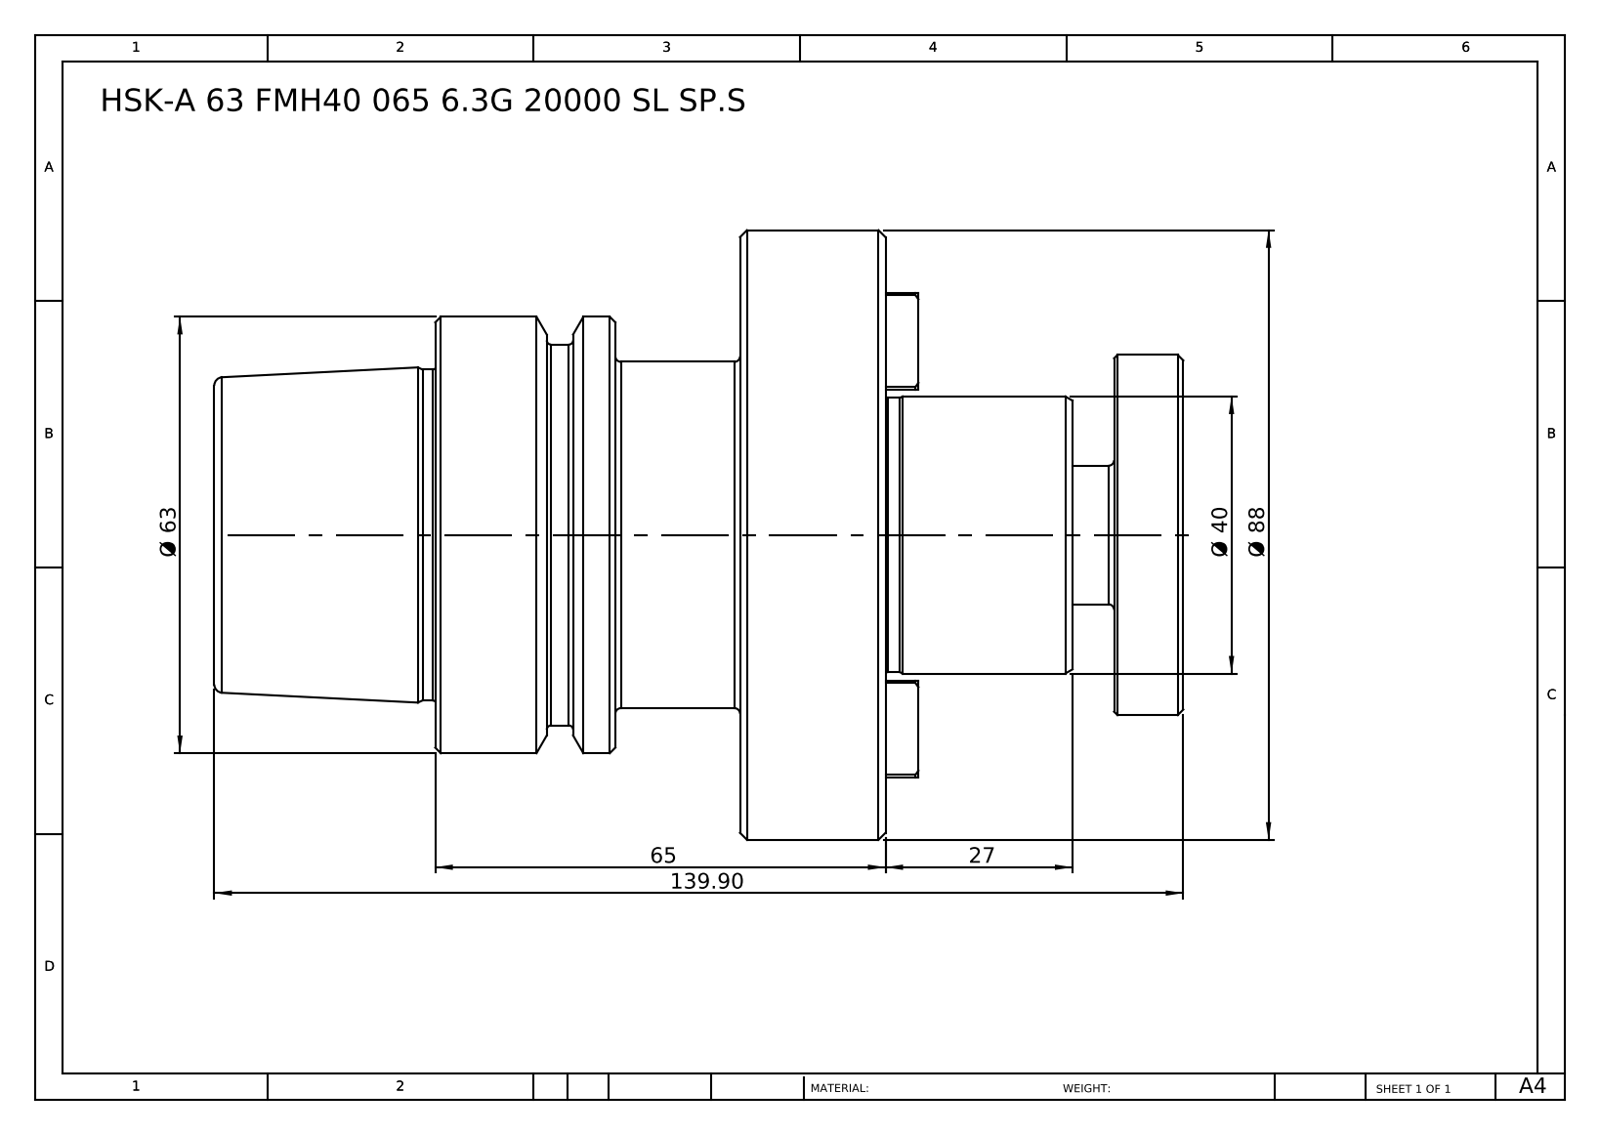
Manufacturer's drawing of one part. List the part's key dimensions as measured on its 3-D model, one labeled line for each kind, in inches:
Part name (STEP PRODUCT): HSK-A 63 FMH40 065 6.3G 20000 SL SP.S
STEP written by: SolidWorks 2014 (CONFIG_CONTROL_DESIGN)
Units: inches
Bodies: 1 solid, 102 faces (38 planar, 20 cylindrical, 44 other)
Overall size (bounding box): 5.508 × 3.465 × 3.465
Volume: 21.62 in³ · Surface area: 65.66 in²
Round bosses / shafts (diameter × count): ⌀3.465 ×1, ⌀2.48 ×1, ⌀2.165 ×1, ⌀2.047 ×1, ⌀1.969 ×1, ⌀1.881 ×1, ⌀1.575 ×1, ⌀1.559 ×1
Main face-to-face distances: 0.827, 1.693, 2.52, 0.394, 1.299, 2.126, 2.988, 5.508, 5.114, 3.815
